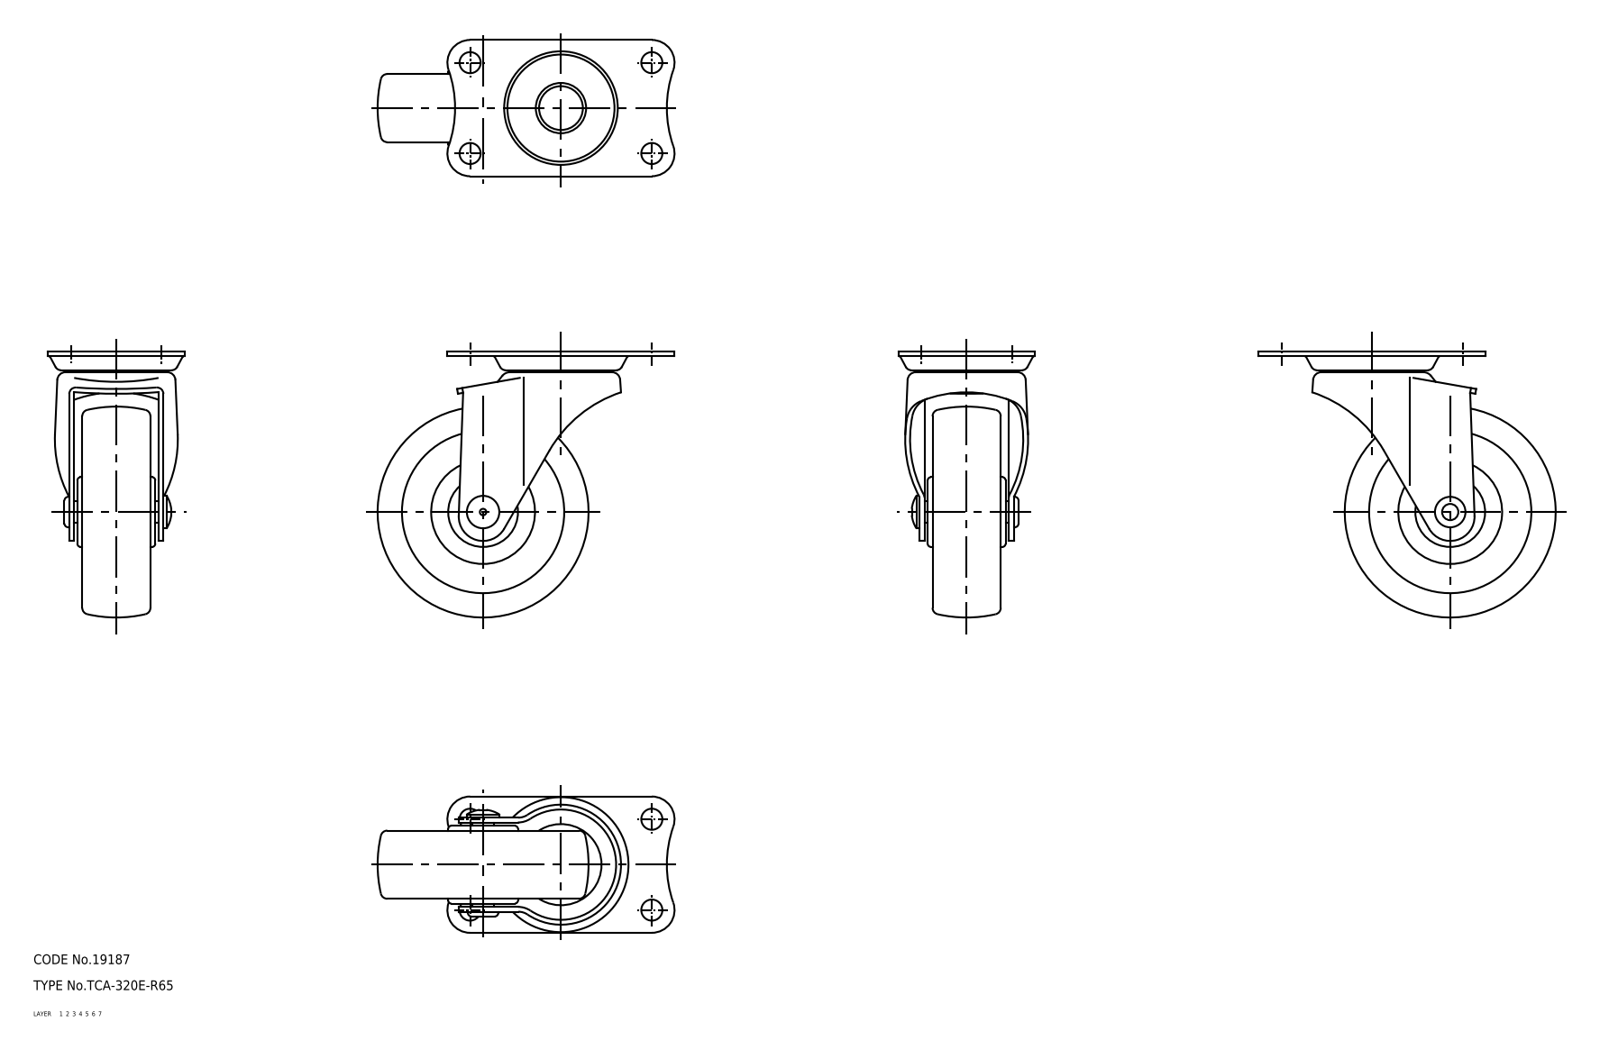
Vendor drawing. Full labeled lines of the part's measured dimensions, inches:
Part name (STEP PRODUCT): wheel; mounting plate; main shaft; axle (+1 more)
STEP written by: CADfix (AUTOMOTIVE_DESIGN)
Units: inches
Bodies: 5 solids, 236 faces (0 planar, 0 cylindrical, 236 other)
Overall size (bounding box): 3.602 × 3.228 × 1.654
Volume: 4.918 in³ · Surface area: 45.92 in²
